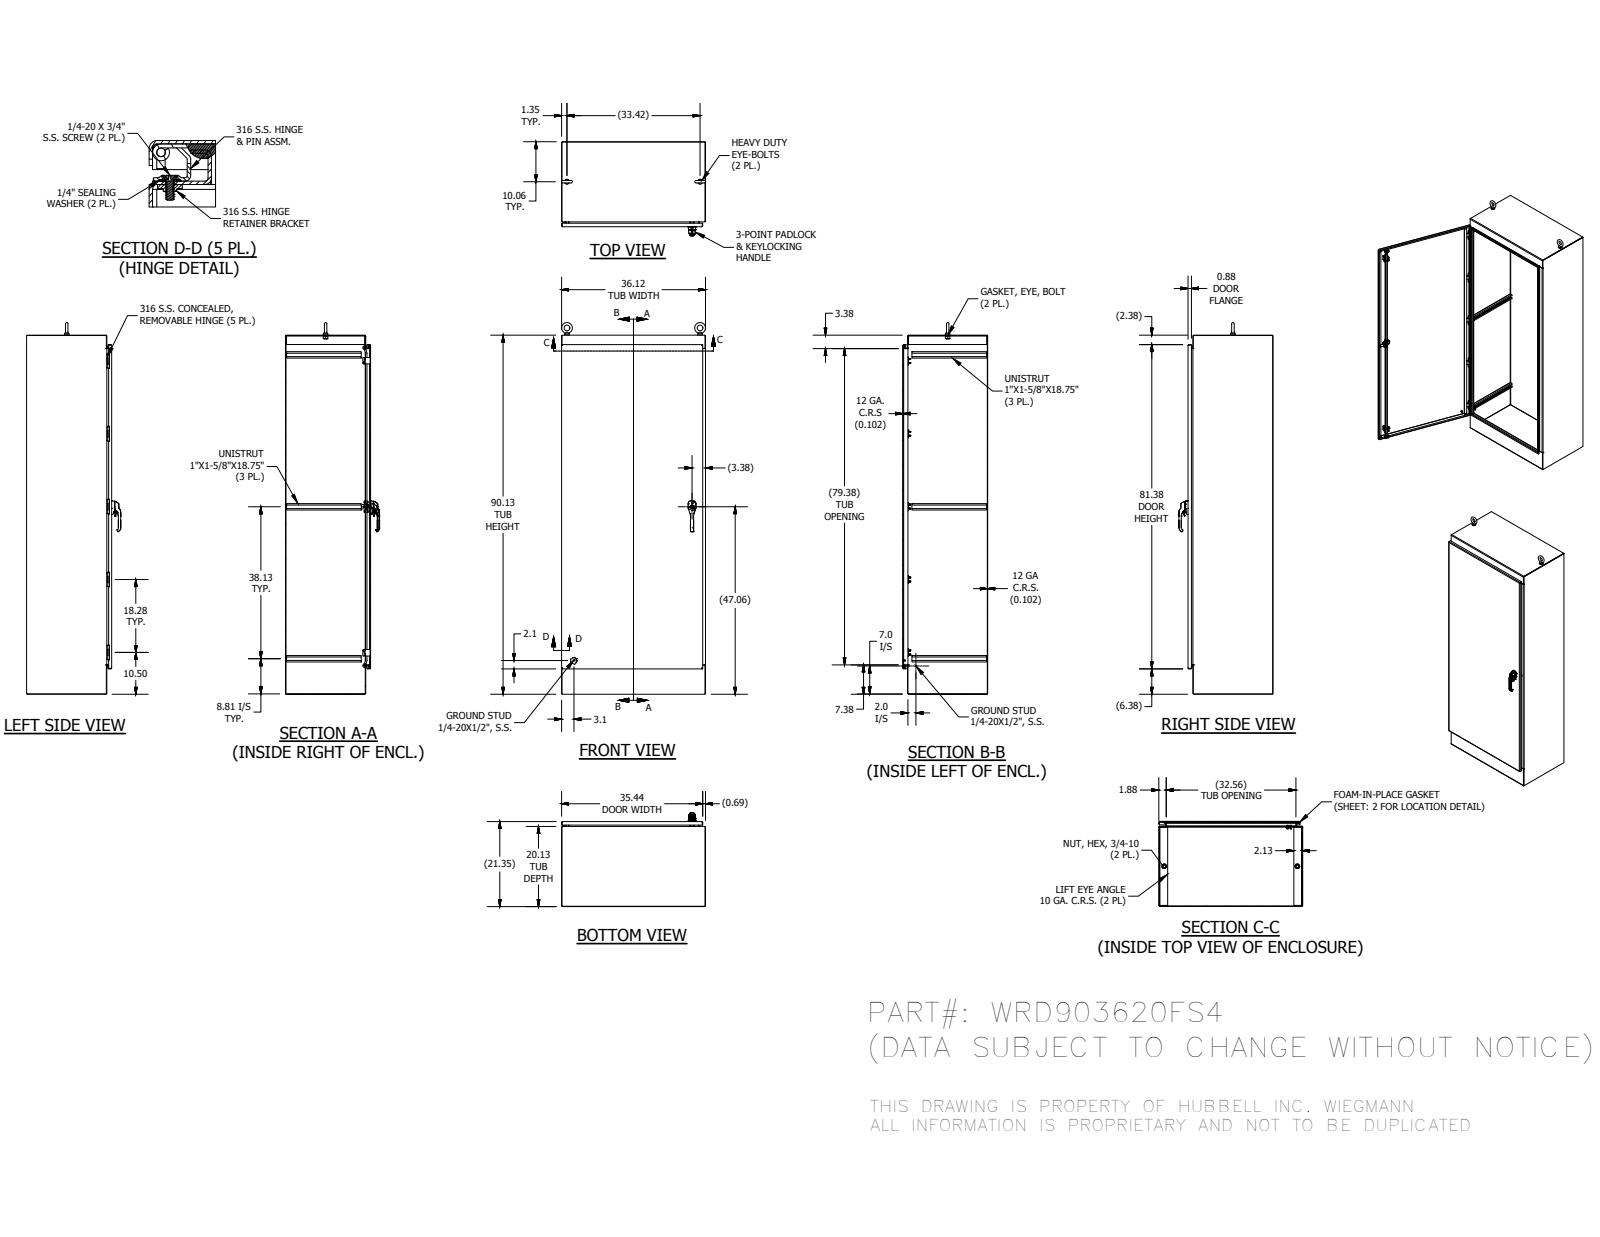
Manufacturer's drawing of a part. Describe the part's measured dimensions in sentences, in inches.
The part is named "WRD903620FS4BLS; WRD3620FS4TOP; WRD3620FS4BTM; WRD9036FS4DR (+8 more)". Its 3-D file was written by "Autodesk Inventor 2016 (AUTOMOTIVE_DESIGN)". It is 94 solids with 3829 faces: 1580 planar, 1269 cylindrical and 980 other. Overall it measures 93.248 by 36.127 by 23.616 inches. Its volume is 1 412 cubic inches and its surface area 27 030 square inches. Round holes: 10 of diameter 0.23, 10 of diameter 0.281, 10 of diameter 0.65, 8 of diameter 0.276, 4 of diameter 0.2, 3 of diameter 0.213, 3 of diameter 0.236, 3 of diameter 0.28, 2 of diameter 0.241, 2 of diameter 0.25, 2 of diameter 0.252, 2 of diameter 0.4. Round bosses or shafts: 18 of diameter 0.25, 10 of diameter 0.625, 10 of diameter 0.404, 10 of diameter 0.182, 2 of diameter 1.25, 2 of diameter 1.12, 2 of diameter 1, 2 of diameter 0.75. Partial cylindrical surfaces (rounded edges, fillets, slot ends): 164 of radius 0.02, 86 of radius 0.012, 33 of radius 0.063, 26 of radius 0.01, 22 of radius 0.125, 19 of radius 0.019, 15 of radius 0.079, 14 of radius 0.05. The main face-to-face distances are 0.102, 21.245, 36.023, 21.143, 21.347, 35.921, 36.125, 90.023, 20.023, 1.222. The hole center spacings are 1, 0.492, 18.281, 18.281, 36.563, 54.844, 0.256, 0.886.
